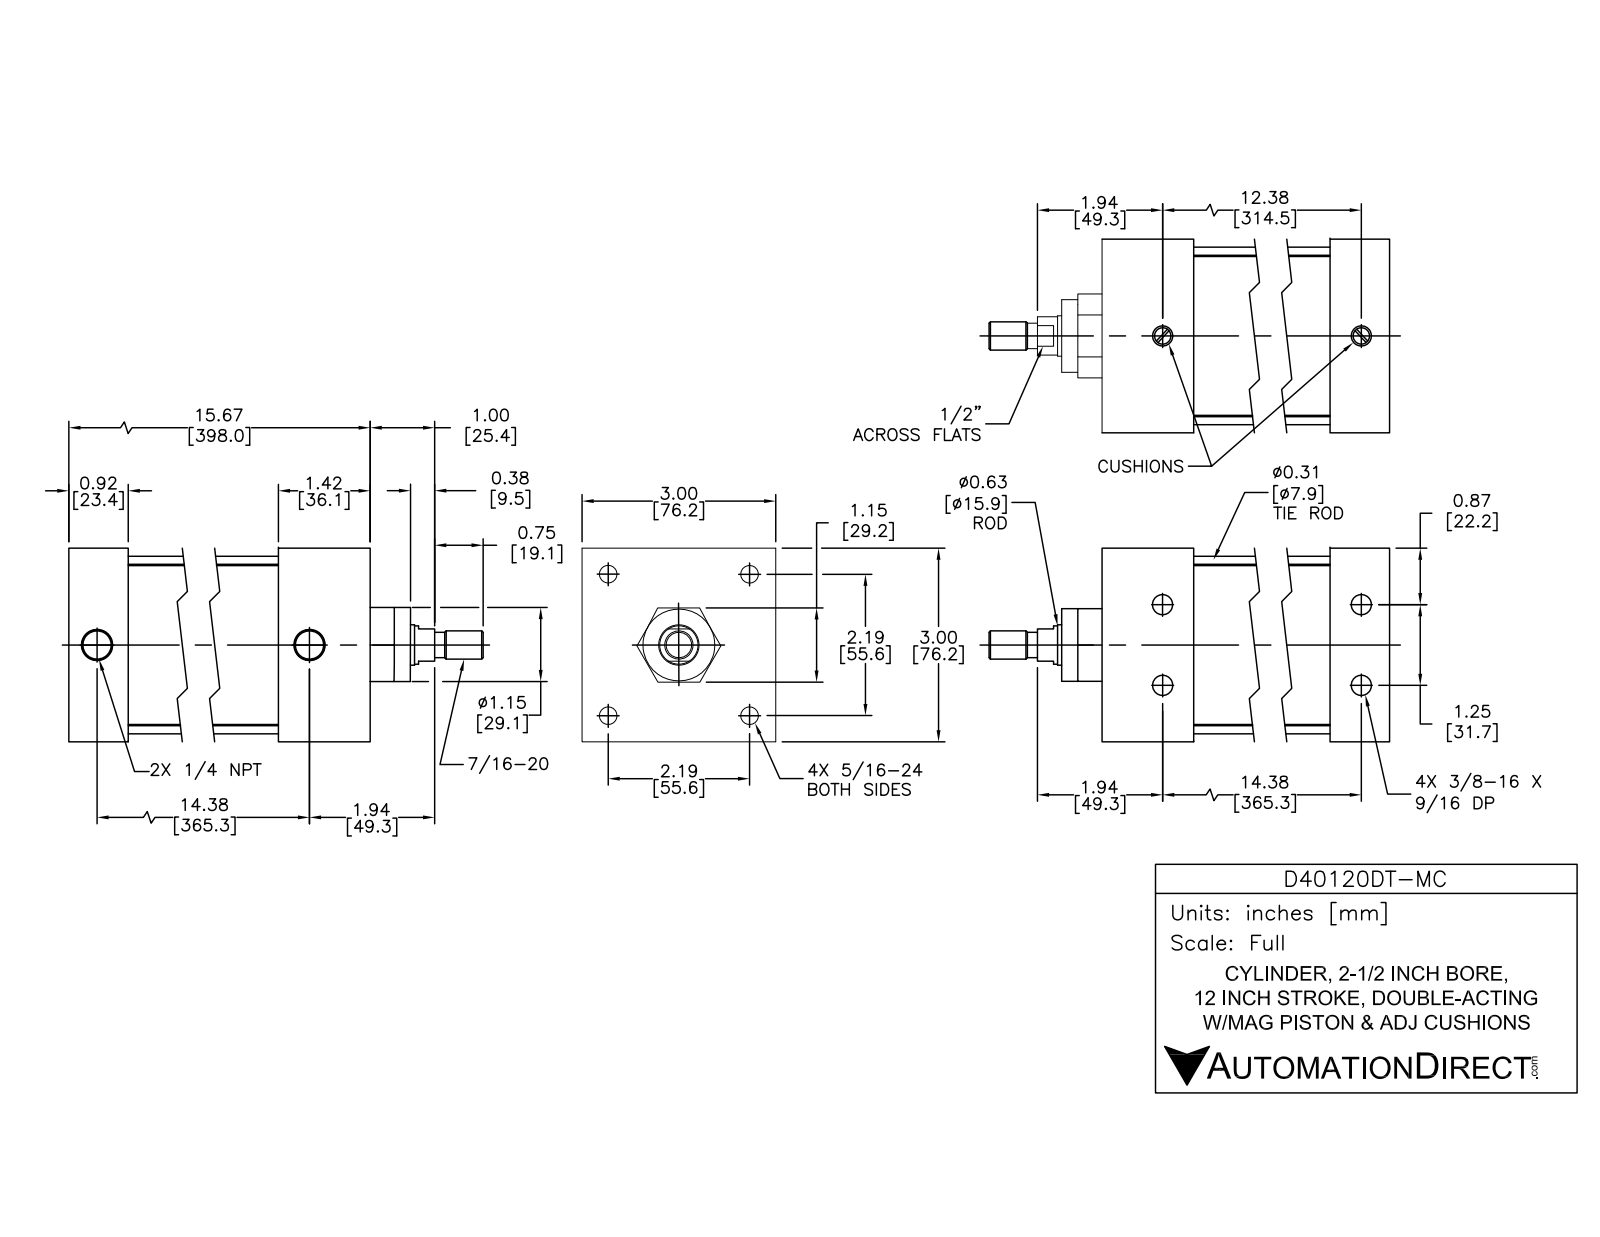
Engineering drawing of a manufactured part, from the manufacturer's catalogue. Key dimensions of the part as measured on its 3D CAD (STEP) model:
Part name (STEP PRODUCT): D40120DT-MC; D40120DT-M PISTON; D40120DT-M BODY
STEP written by: SolidWorks 2015 (AUTOMOTIVE_DESIGN)
Units: inches
Bodies: 12 solids, 298 faces (94 planar, 114 cylindrical, 90 other)
Overall size (bounding box): 17.496 × 3 × 3
Volume: 48.23 in³ · Surface area: 416.6 in²
Round holes (diameter × count): ⌀0.267 ×4, ⌀0.307 ×4, ⌀0.359 ×4, ⌀0.5 ×4, ⌀0.297 ×2, ⌀0.477 ×2, ⌀0.625 ×1, ⌀0.628 ×1, ⌀2.5 ×1
Round bosses / shafts (diameter × count): ⌀0.484 ×4, ⌀0.313 ×4, ⌀0.282 ×4, ⌀2.75 ×1, ⌀2.497 ×1, ⌀1.12 ×1, ⌀0.622 ×1, ⌀0.59 ×1
Partial cylindrical surfaces — rounded edges, fillets, slot ends (radius × count): R0.3 ×4
Main face-to-face distances: 3, 0.08, 13.326, 15.746, 14.726, 1.02, 1.42, 13.306, 14.326, 1
Hole centre spacings: 1.556, 2.2, 14.37, 0.625, 0.625, 1.25, 3.111, 14.383
